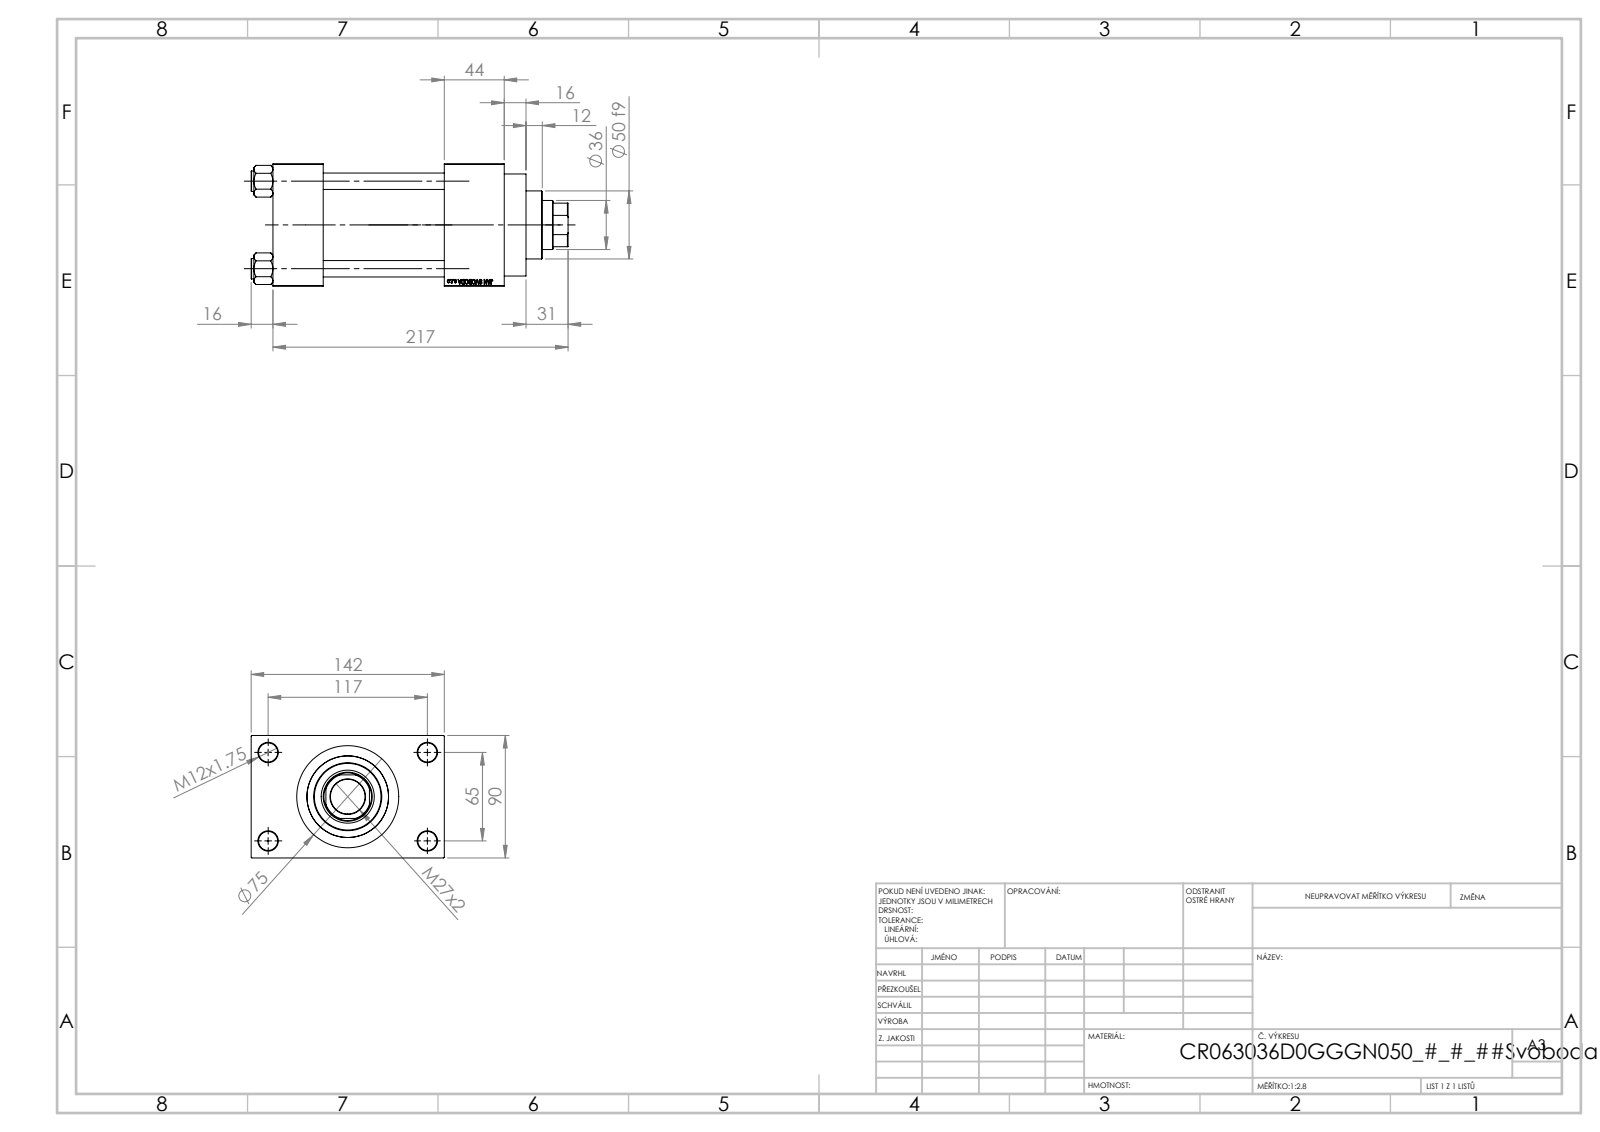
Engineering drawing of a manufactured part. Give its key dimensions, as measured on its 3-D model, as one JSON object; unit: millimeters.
{"part_name": "V215_VC_A; NUT_M5_D; V215CR_D_Body; V215CR_D_TYCINKA (+1 more)", "step_written_by": "SolidWorks 2019 (CONFIG_CONTROL_DESIGN)", "units": "millimeters", "bodies": {"solids": 11, "faces": 1104, "planar": 497, "cylindrical": 89, "other": 518}, "overall_size": [233, 142, 90], "volume_mm3": 1183000, "surface_area_mm2": 224435, "round_holes": [[12, 4], [14, 4], [7, 2], [20.96, 2], [30, 2], [25.5, 1], [36, 1], [39, 1], [50, 1], [60, 1], [63, 1]], "round_bosses_or_shafts": [[15, 4], [75, 1], [69, 1]], "partial_cylinders_radius": [[17.5, 1]], "face_to_face_distances": [90, 89, 37, 126, 170, 133, 44, 26, 116, 142], "hole_center_spacings": [26.35, 45.47, 64.3, 66.92, 69.81, 90.65, 111.34, 65]}
